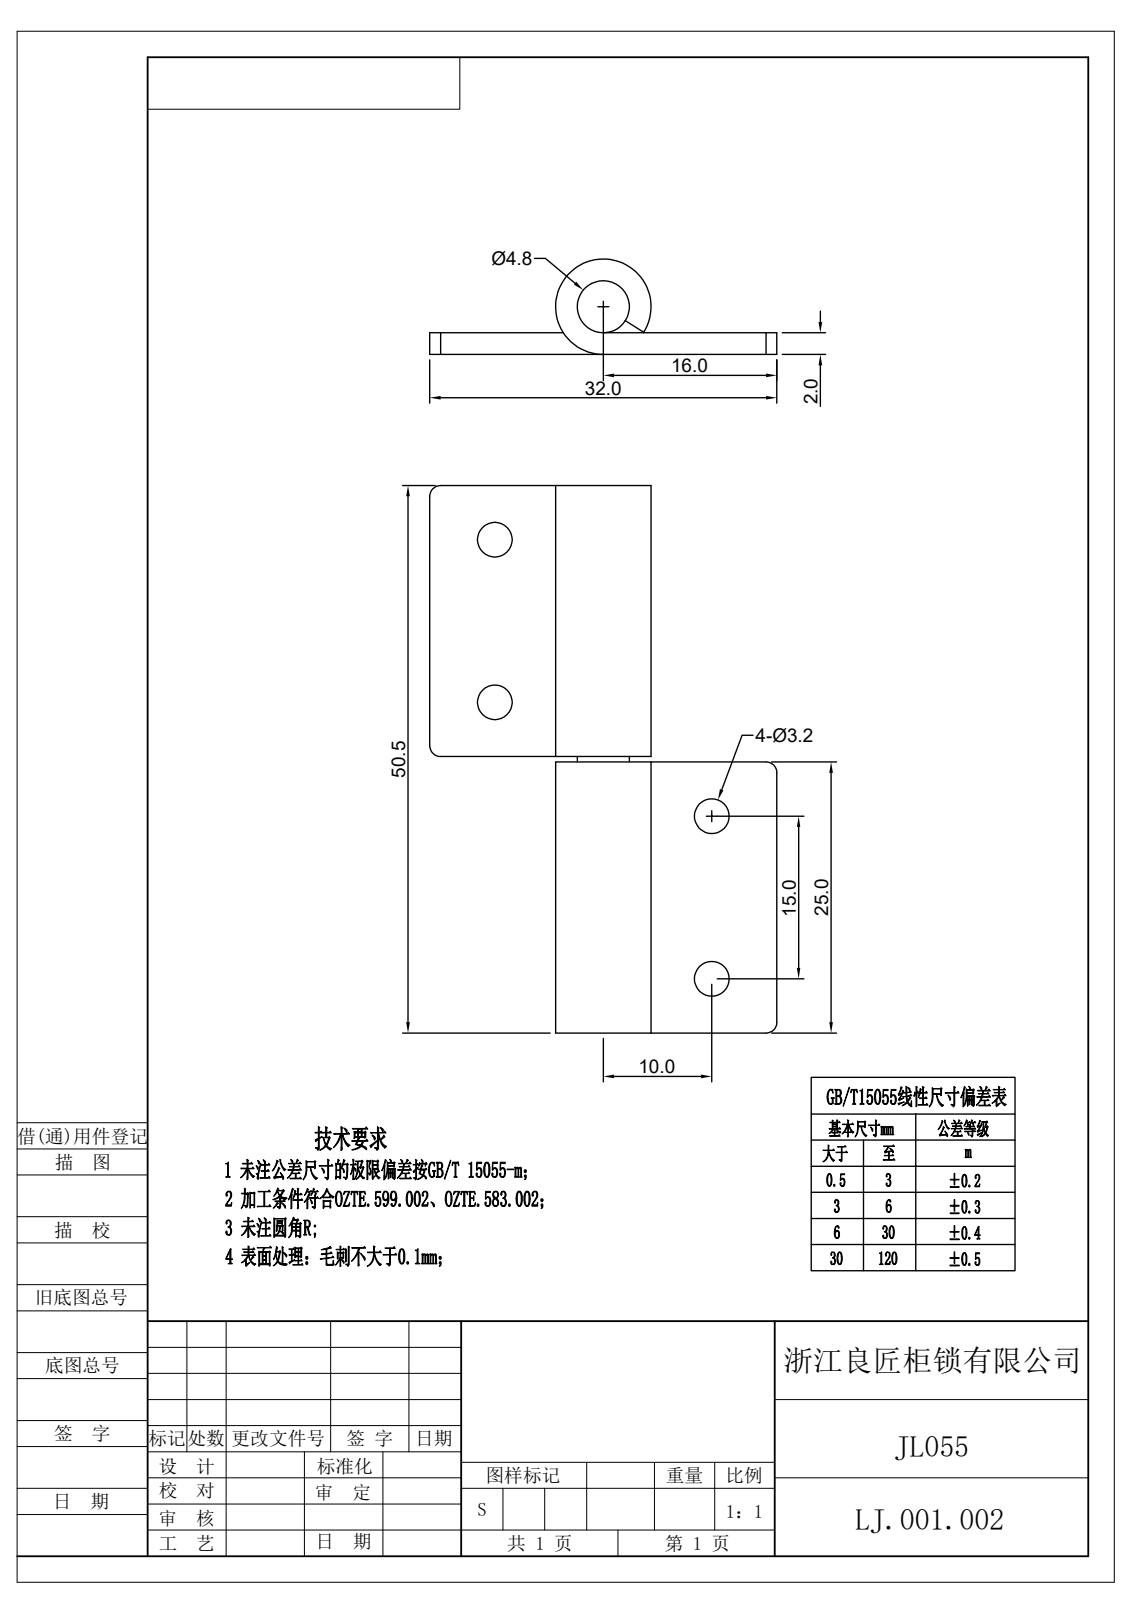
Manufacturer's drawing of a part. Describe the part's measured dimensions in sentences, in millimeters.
Its 3-D file was written by "Rhino 8.5 (CONFIG_CONTROL_DESIGN)". It is 3 solids with 32 faces: 14 planar, 18 cylindrical and 0 other. Overall it measures 50.5 by 32 by 8.8 millimeters. Its volume is 4 242 cubic millimeters and its surface area 4 674 square millimeters. Round holes: 4 of diameter 3.2, 1 of diameter 4.8. Round bosses or shafts: 1 of diameter 8.8. Partial cylindrical surfaces (rounded edges, fillets, slot ends): 4 of radius 1. The main face-to-face distances are 2, 25, 25.5, 50.5, 0.5, 32. The hole center spacings are 15, 32.41, 22.59, 45.17.
